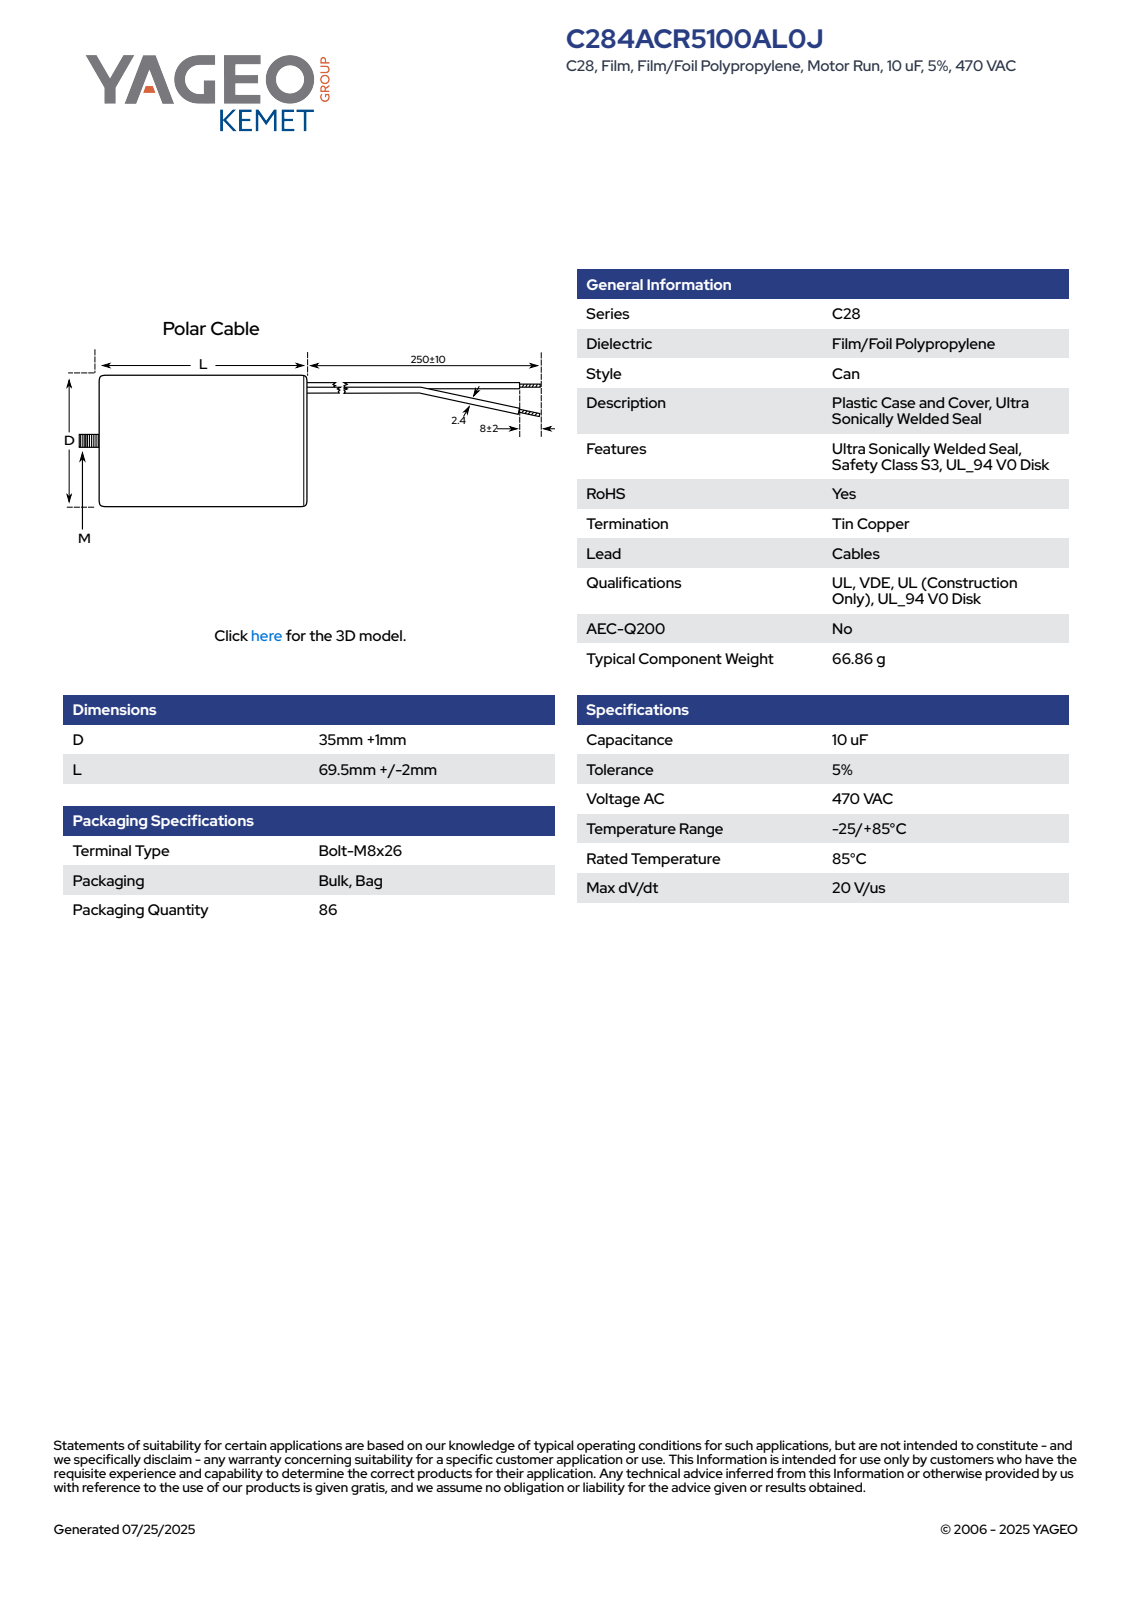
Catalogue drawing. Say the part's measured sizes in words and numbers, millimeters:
The part is named "CFM_C28P_35X69.5_D36L71.5". Its 3-D file was written by "SolidWorks 2021 (AUTOMOTIVE_DESIGN)". It is 1 solid with 76 faces: 26 planar, 15 cylindrical and 35 other. Overall it measures 81.5 by 36.01 by 36 millimeters. Its volume is 71 625 cubic millimeters and its surface area 10 478 square millimeters. Round holes: 1 of diameter 32. Round bosses or shafts: 1 of diameter 36, 1 of diameter 8. Partial cylindrical surfaces (rounded edges, fillets, slot ends): 1 of radius 18.01. The main face-to-face distances are 69.5, 71.5, 2, 10, 79.5, 81.5.
